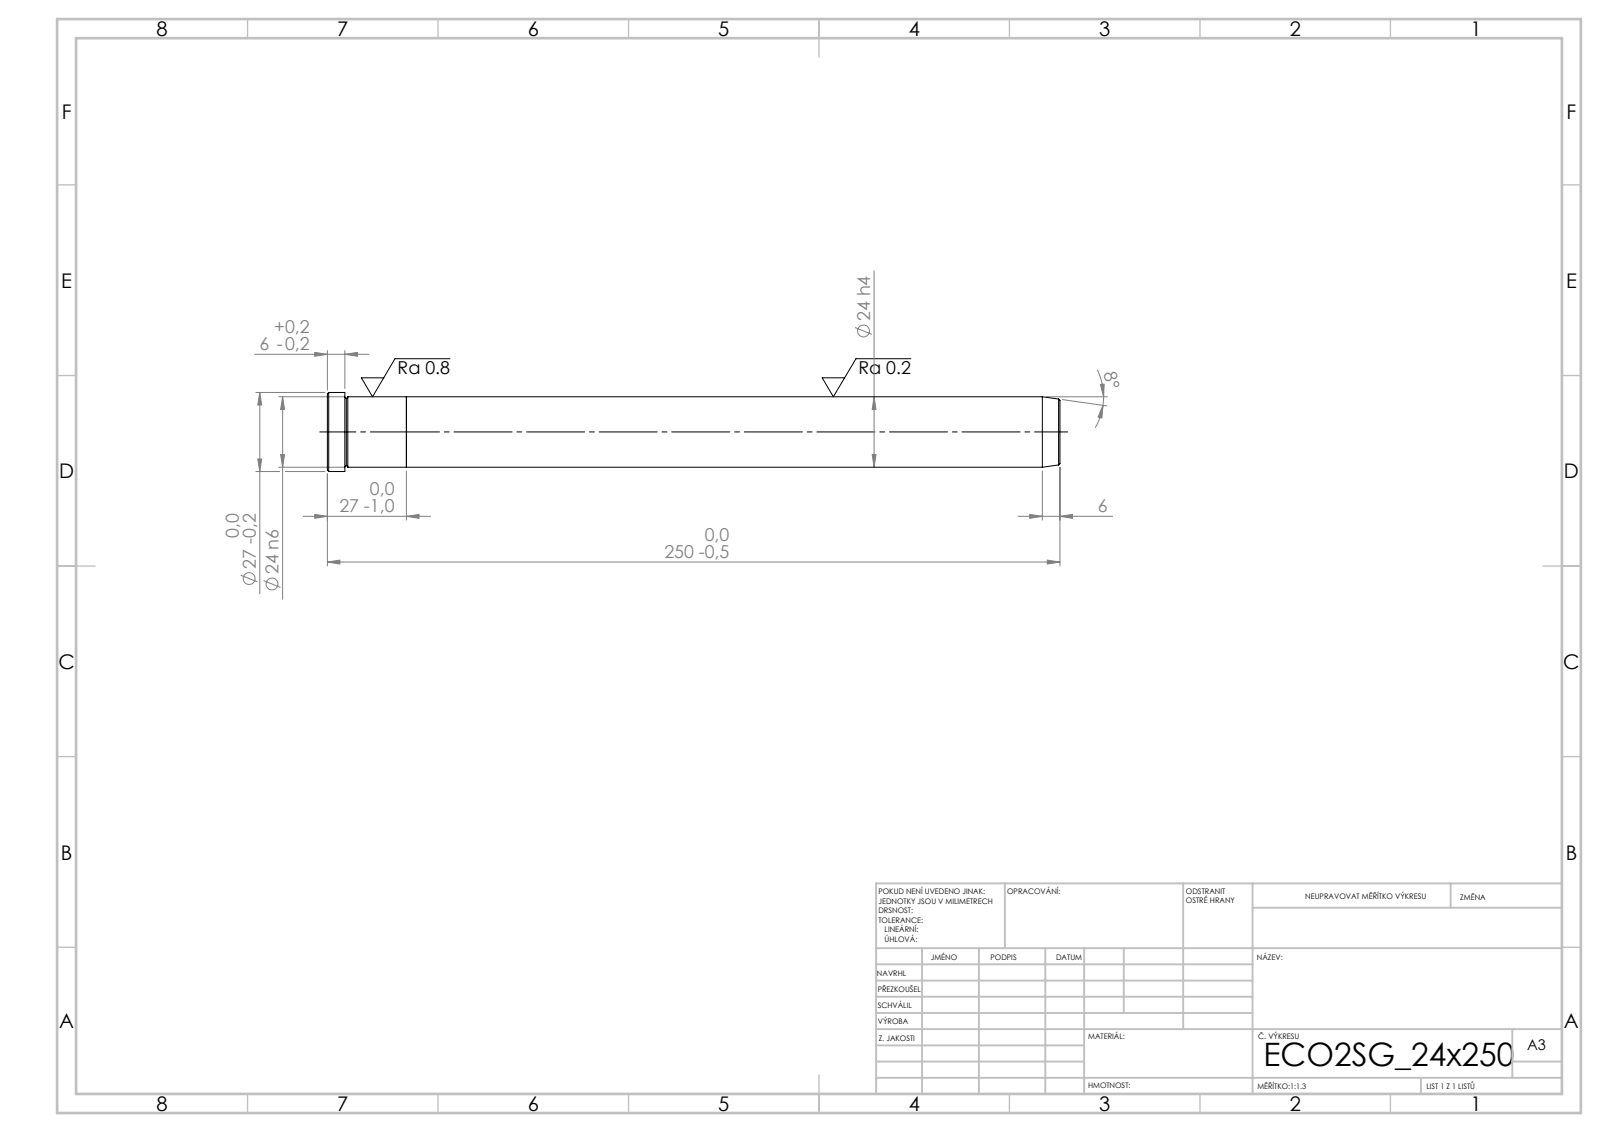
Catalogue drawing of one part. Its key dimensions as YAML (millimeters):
step_written_by: "SolidWorks 2019 (CONFIG_CONTROL_DESIGN)"
units: millimeters
bodies: {solids: 2, faces: 21, planar: 5, cylindrical: 6, other: 10}
overall_size: [250, 27, 27]
volume: 113590
surface_area: 20887
round_bosses_or_shafts:
  - {diameter: 27, count: 1}
  - {diameter: 24, count: 1}
face_to_face_distances: [27, 223, 250, 244, 21, 6]
